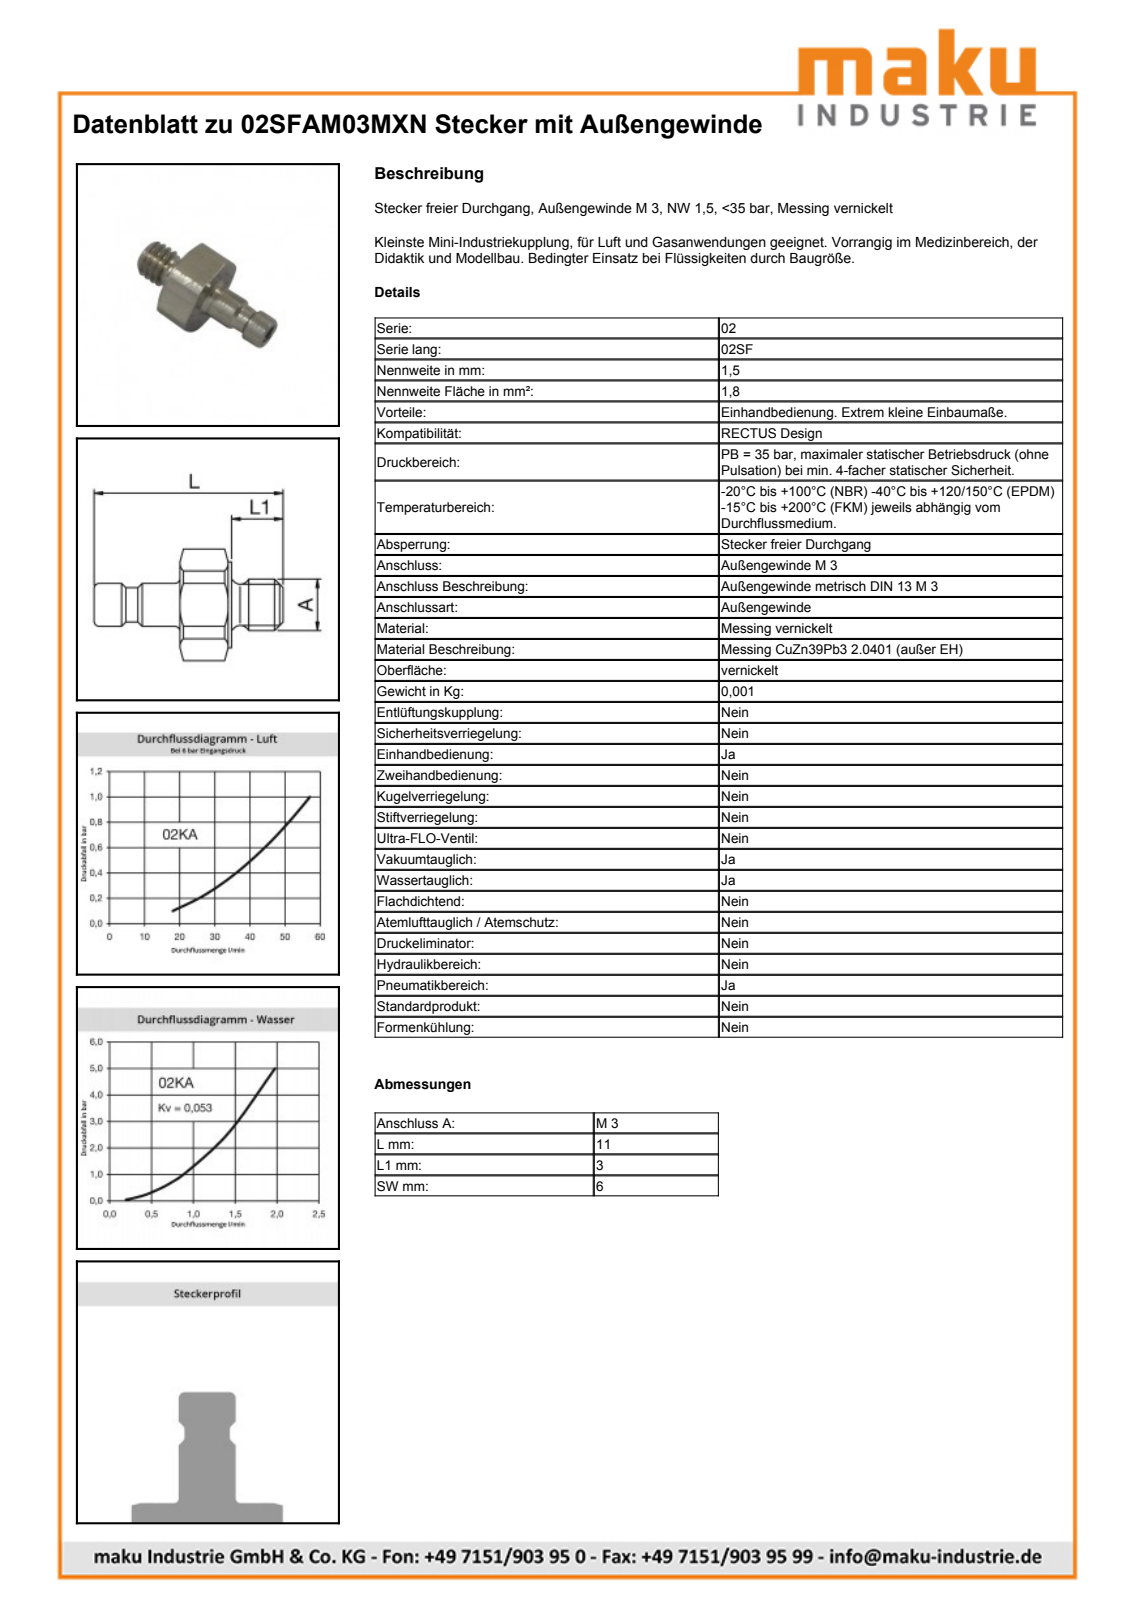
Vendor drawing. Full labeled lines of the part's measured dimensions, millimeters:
Part name (STEP PRODUCT): D109636
STEP written by: Autodesk Inventor 2013 (AUTOMOTIVE_DESIGN)
Units: millimetres
Bodies: 1 solid, 68 faces (17 planar, 18 cylindrical, 33 other)
Overall size (bounding box): 11 × 6.5 × 6
Volume: 112 mm³ · Surface area: 233 mm²
Round holes (diameter × count): ⌀1.5 ×1
Round bosses / shafts (diameter × count): ⌀5 ×1, ⌀3 ×1, ⌀2.54 ×1, ⌀2 ×1
Partial cylindrical surfaces — rounded edges, fillets, slot ends (radius × count): R3.25 ×1
Main face-to-face distances: 6, 3, 2.8, 5, 7.8, 8, 11, 3.2
